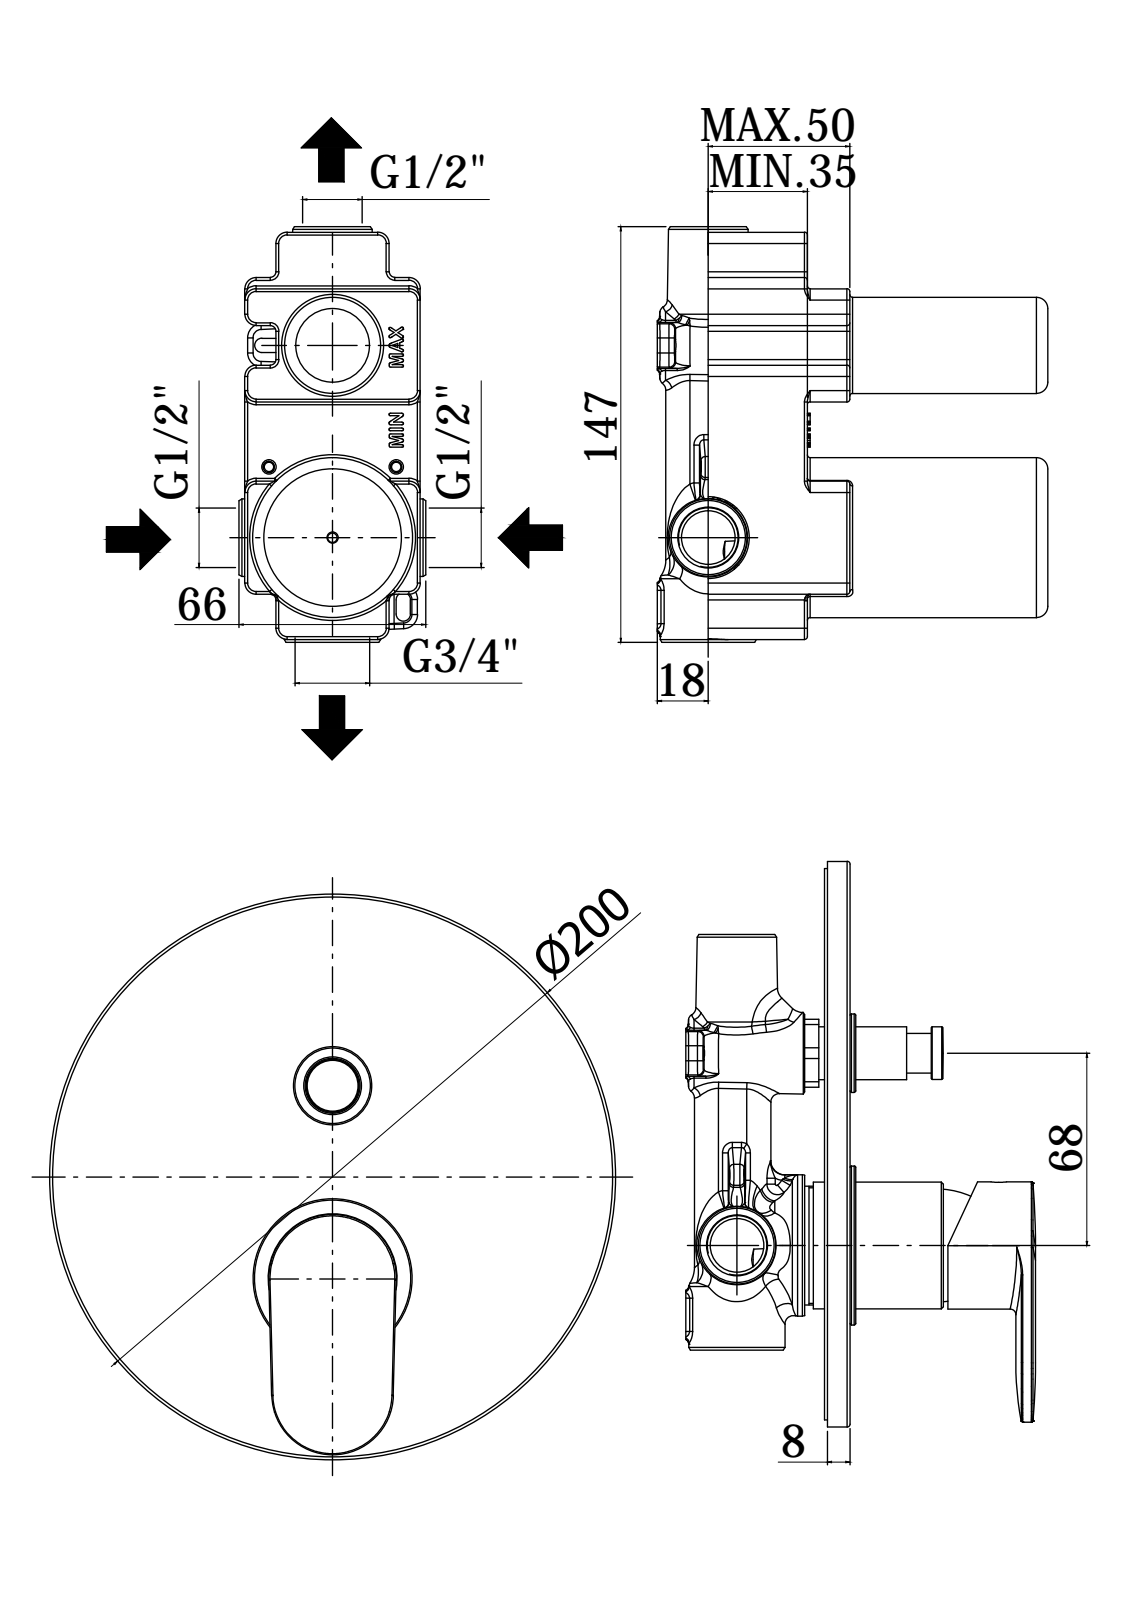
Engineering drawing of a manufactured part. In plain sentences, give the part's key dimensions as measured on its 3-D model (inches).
The part is named "CA015CR". Its 3-D file was written by "CREO PARAMETRIC BY PTC INC, 2020044 (CONFIG_CONTROL_DESIGN)". It is 2 solids with 159 faces: 43 planar, 46 cylindrical and 70 other. Overall it measures 7.874 by 7.874 by 2.61 inches. Its volume is 18.26 cubic inches and its surface area 145.9 square inches. Round holes: 1 of diameter 0.118, 1 of diameter 0.177, 1 of diameter 0.217, 1 of diameter 1.205, 1 of diameter 1.417, 1 of diameter 1.476. Round bosses or shafts: 1 of diameter 7.874, 1 of diameter 2.213, 1 of diameter 1.772, 1 of diameter 1.764, 1 of diameter 1.091, 1 of diameter 0.736, 1 of diameter 0.732, 1 of diameter 0.551. Partial cylindrical surfaces (rounded edges, fillets, slot ends): 4 of radius 0.118, 1 of radius 0.138, 1 of radius 0.846. The main face-to-face distances are 0.315, 0.079, 0.394, 2.098, 2.492, 2.177, 0.096, 0.455, 0.925, 1.004.
